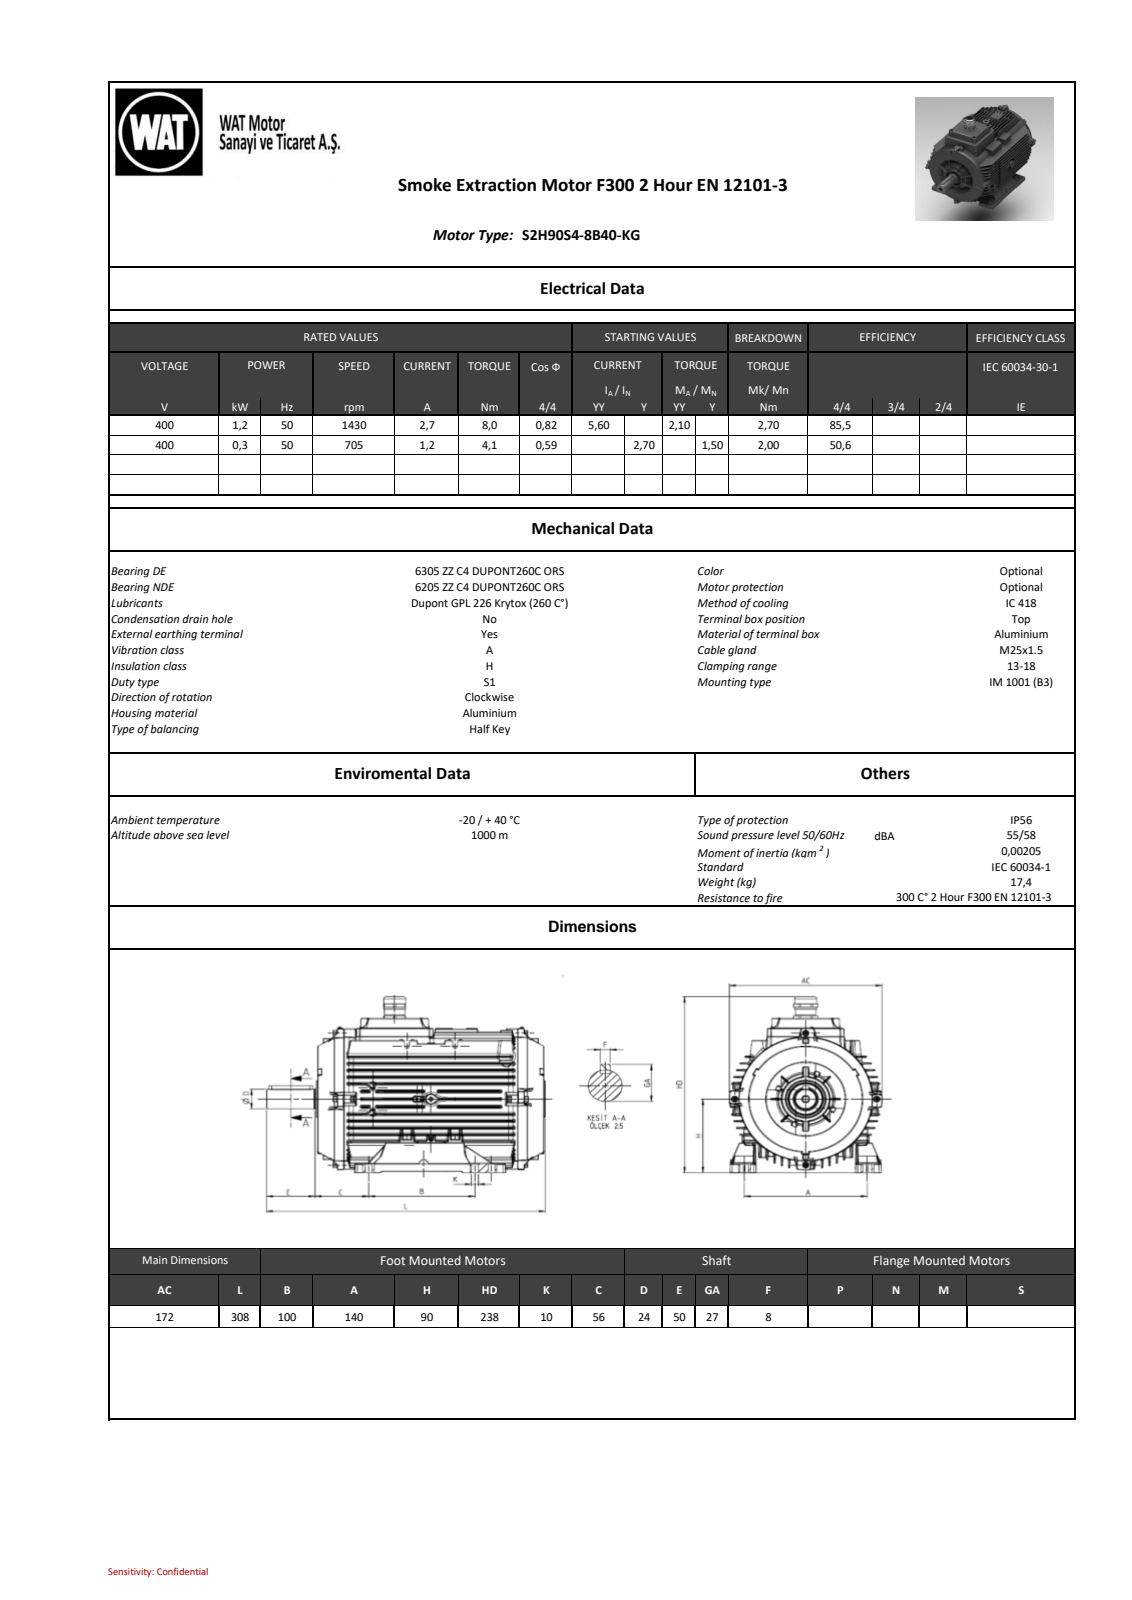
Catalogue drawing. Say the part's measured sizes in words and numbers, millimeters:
The part is named "2603BE5CCA1Cd441". Its 3-D file was written by "SIEMENS PLM Software NX 11.0 (AUTOMOTIVE_DESIGN)". It is 0 solids with 6679 faces: 1385 planar, 2249 cylindrical and 3045 other. Overall it measures 307.75 by 238 by 172.47 millimeters. Round holes: 4 of diameter 3.5, 1 of diameter 6.8, 1 of diameter 8.4, 1 of diameter 18, 1 of diameter 32, 1 of diameter 36.9, 1 of diameter 37.1, 1 of diameter 40. Round bosses or shafts: 8 of diameter 9.2, 8 of diameter 8.5, 4 of diameter 8, 4 of diameter 5, 1 of diameter 29.59, 1 of diameter 28.14, 1 of diameter 26.62, 1 of diameter 25. Partial cylindrical surfaces (rounded edges, fillets, slot ends): 576 of radius 1, 569 of radius 0.8, 113 of radius 0.5, 64 of radius 2, 61 of radius 0.98, 59 of radius 0.2, 28 of radius 8, 18 of radius 1.5. The main face-to-face distances are 91.91, 7.5, 7.37, 23.57, 7.94, 82.85, 9.06, 16.43, 50.35, 74.81. The hole center spacings are 13, 147.54.
